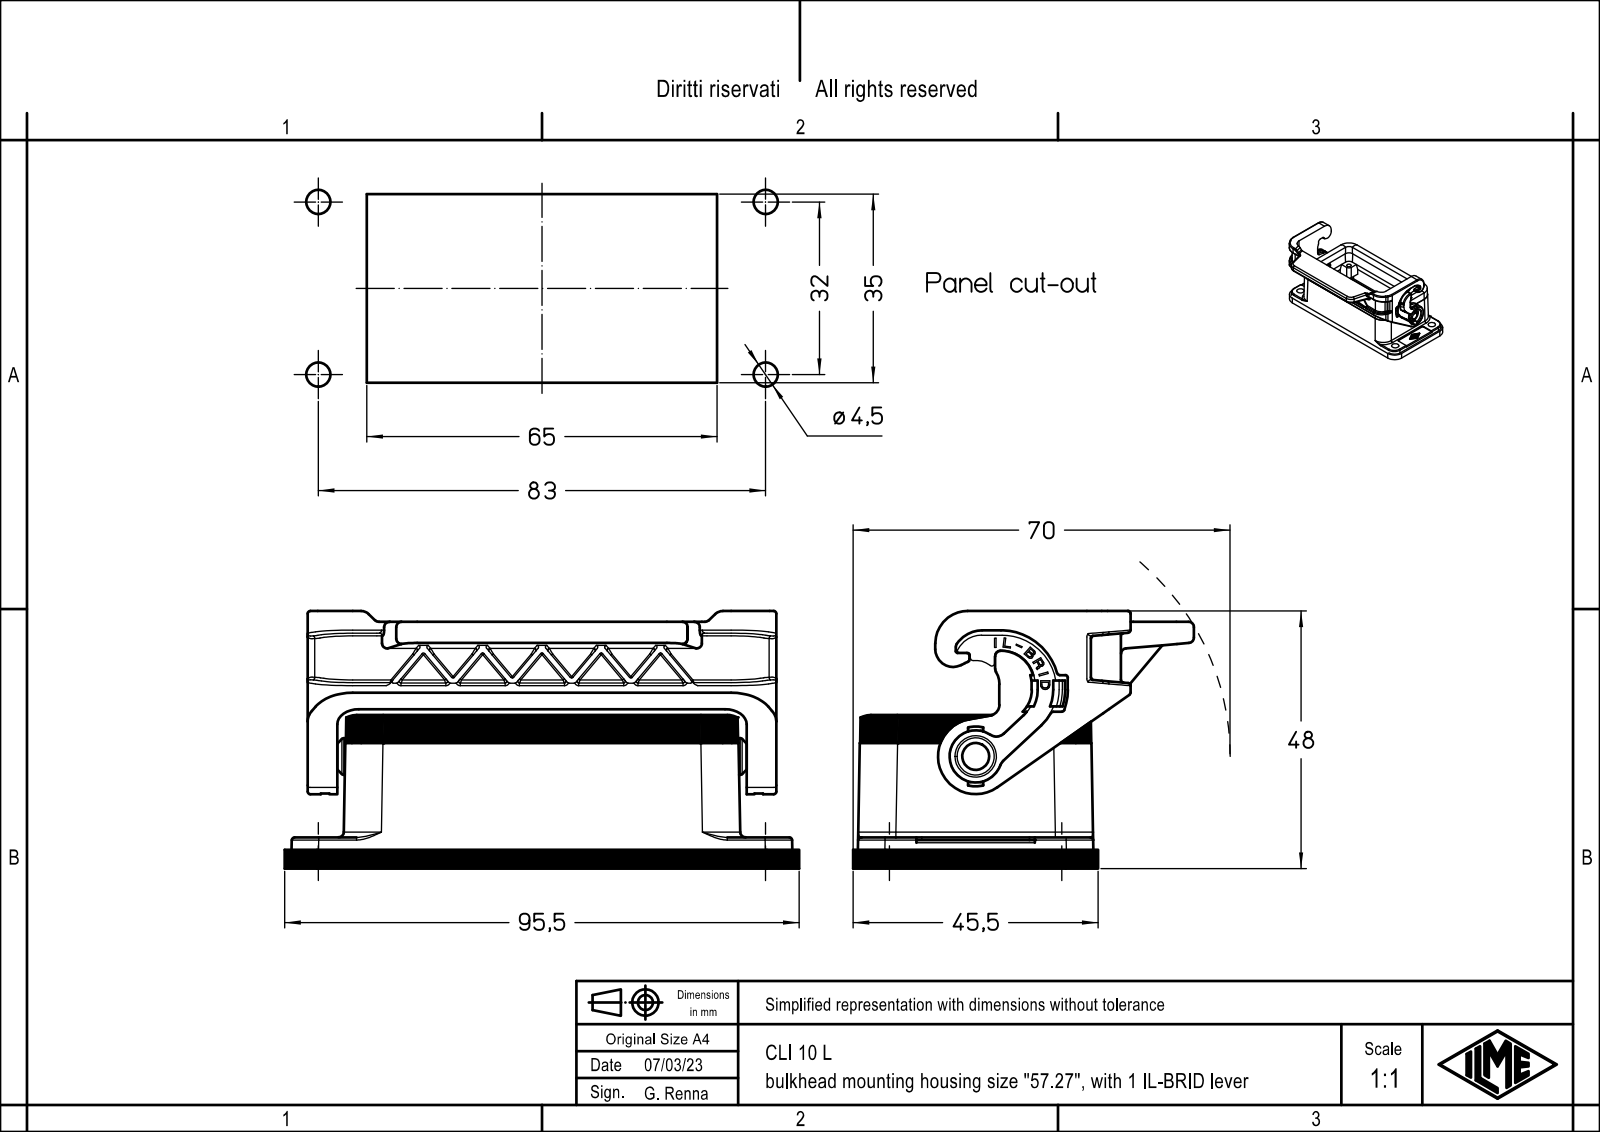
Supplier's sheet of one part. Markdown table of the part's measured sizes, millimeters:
| quantity | value |
| --- | --- |
| part name | CLI 10 L |
| STEP written by | Creo Elements/Direct Modeling 20.1B 02-Apr-2019 (C) Parametric Technology GmbH (AUTOMOTIVE_DESIGN) |
| units | millimeters |
| bodies | 1 solid, 1020 faces (655 planar, 277 cylindrical, 88 other) |
| overall size | 95.5 × 63.25 × 47.8 |
| volume | 42 456 mm³ |
| surface area | 28 464 mm² |
| round holes (diameter × count) | 3.8 × 4, 4.5 × 4, 3.25 × 1, 5.4 × 1, 7.7 × 1 |
| round bosses / shafts (diameter × count) | 6.9 × 1, 6.8 × 1, 5.2 × 1, 3.2 × 1 |
| partial cylindrical surfaces (radius × count) | 0.1 × 27, 1 × 18, 0.17 × 15, 0.2 × 15, 2 × 13, 4 × 12, 0.5 × 11, 7 × 10 |
| main face-to-face distances | 3.03, 5.5, 81.5, 45.8, 40.5, 3.5, 76, 2, 38.9, 38.96 |
| hole center spacings | 32, 83, 88.96 |
